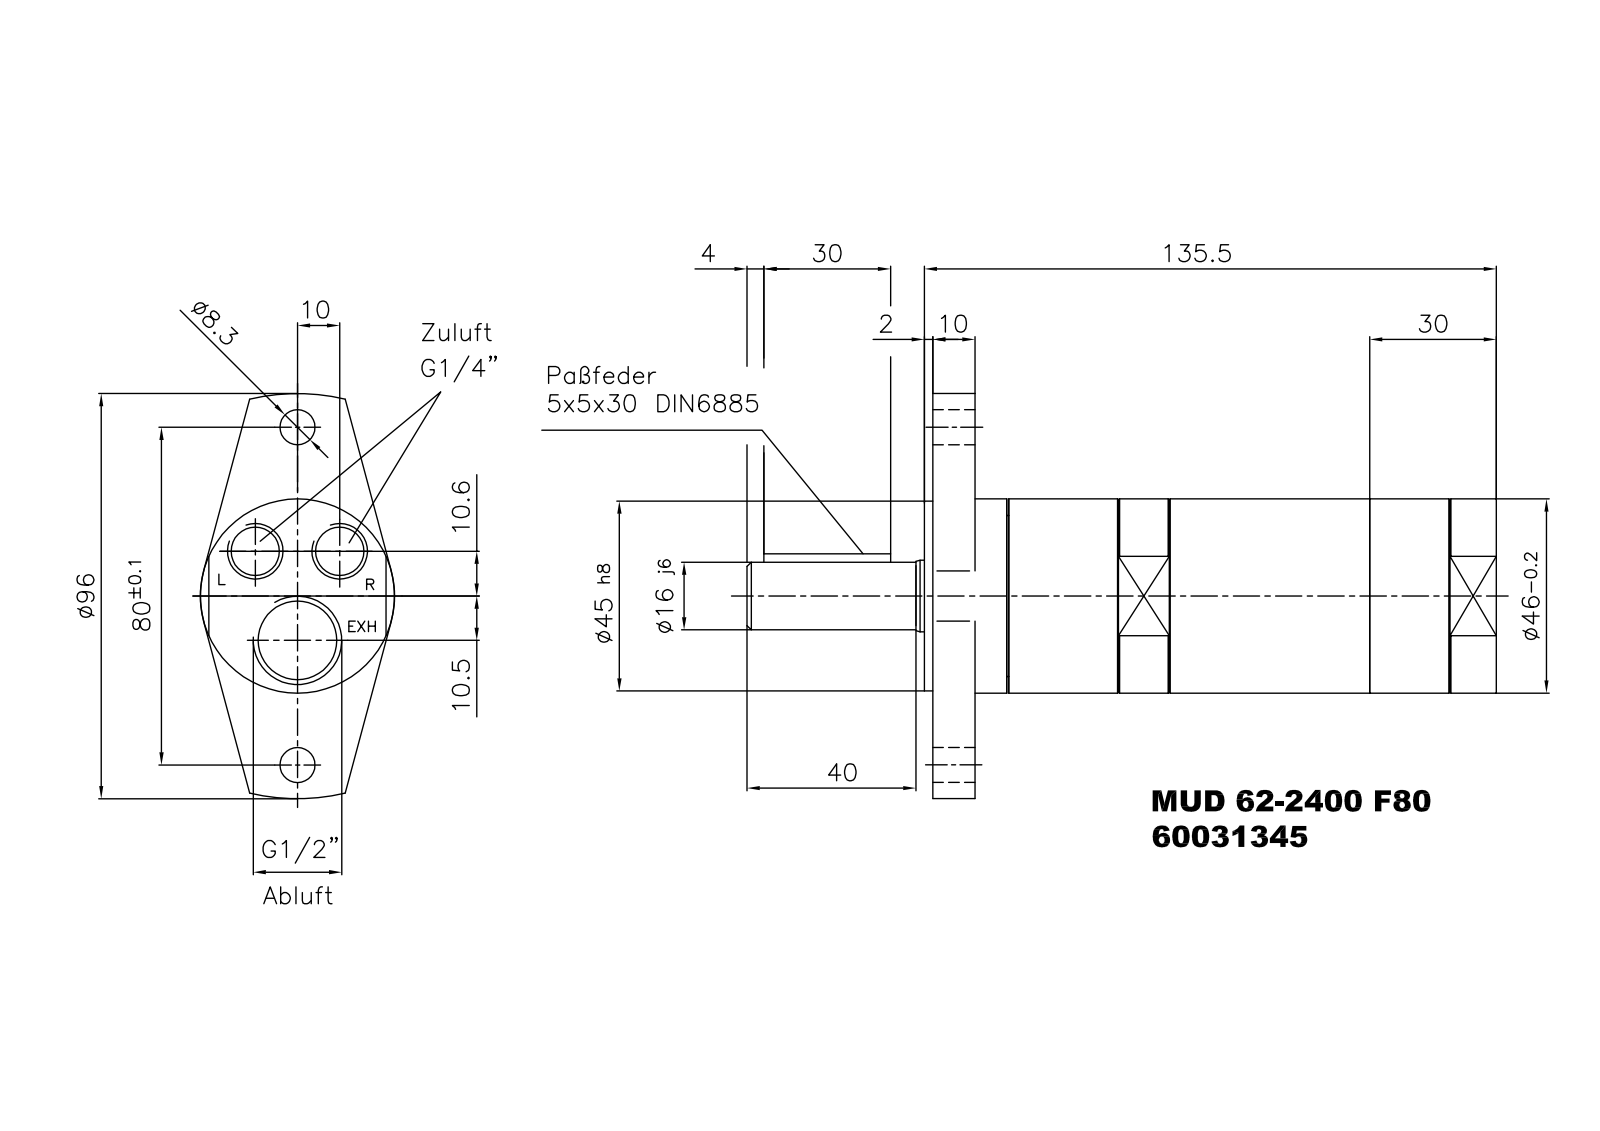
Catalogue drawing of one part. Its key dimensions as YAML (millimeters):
part_name: "MUD 62-8600 2400 1890 1000_F80"
step_written_by: "Autodesk Inventor 2013 (AUTOMOTIVE_DESIGN)"
units: millimeters
bodies: {solids: 2, faces: 179, planar: 114, cylindrical: 23, other: 42}
overall_size: [177.5, 96, 46]
volume: 241380
surface_area: 36274
round_holes:
  - {diameter: 8.3, count: 2}
  - {diameter: 11.45, count: 2}
  - {diameter: 1.6, count: 1}
  - {diameter: 17.5, count: 1}
  - {diameter: 18.63, count: 1}
round_bosses_or_shafts:
  - {diameter: 46, count: 1}
  - {diameter: 45, count: 1}
  - {diameter: 40, count: 1}
  - {diameter: 16.95, count: 1}
  - {diameter: 16, count: 1}
partial_cylinders:
  - {radius: 2.5, count: 2}
  - {radius: 48, count: 1}
face_to_face_distances: [103.5, 10, 93.5, 12, 2, 105.5, 123.5, 135.5, 133.5, 30]
hole_center_spacings: [14.57, 23.35, 31.05, 40, 51.58, 10.5, 20, 29.5]
